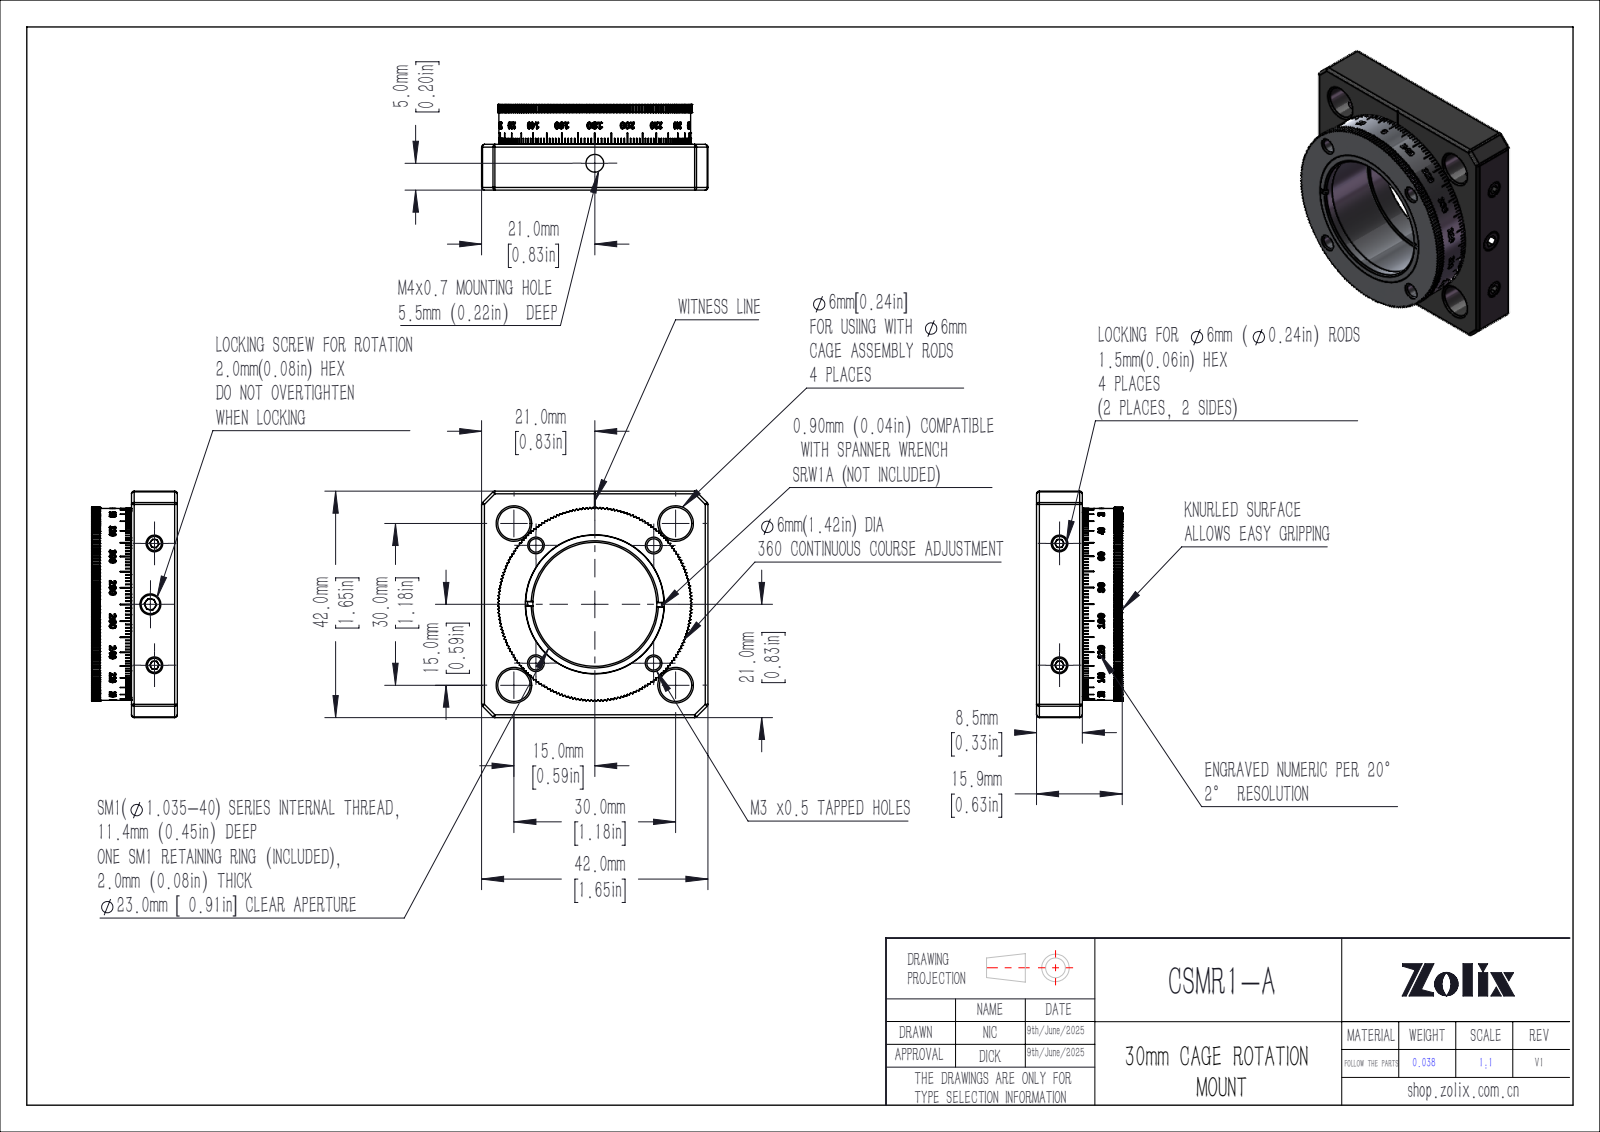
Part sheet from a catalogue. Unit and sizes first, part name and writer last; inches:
Units: inches
Overall size (bounding box): 1.654 × 1.654 × 0.622
Round holes (diameter × count): ⌀0.098 ×6, ⌀0.236 ×4, ⌀0.13 ×2, ⌀0.906 ×1, ⌀0.925 ×1, ⌀0.984 ×1, ⌀1.142 ×1, ⌀1.354 ×1
Round bosses / shafts (diameter × count): ⌀0.118 ×2, ⌀1.402 ×1, ⌀1.346 ×1, ⌀1.339 ×1, ⌀1.035 ×1, ⌀1.031 ×1, ⌀1 ×1, ⌀0.157 ×1
Partial cylindrical surfaces — rounded edges, fillets, slot ends (radius × count): R0.02 ×24, R0.063 ×2, R0.697 ×1
Main face-to-face distances: 0.287, 0.327, 0.098, 0.236, 0.335, 0.622, 0.524, 1.654, 0.091, 0.614
Hole centre spacings: 0.835, 0.86, 1.181, 0.227, 1.034, 1.443, 0.446, 0.608
Volume: 0.828 in³ · Surface area: 17.18 in²
Bodies: 9 solids, 3297 faces (1856 planar, 717 cylindrical, 724 other)
Part name (STEP PRODUCT): CSMR1-A
STEP written by: SolidWorks 2020 (CONFIG_CONTROL_DESIGN)
